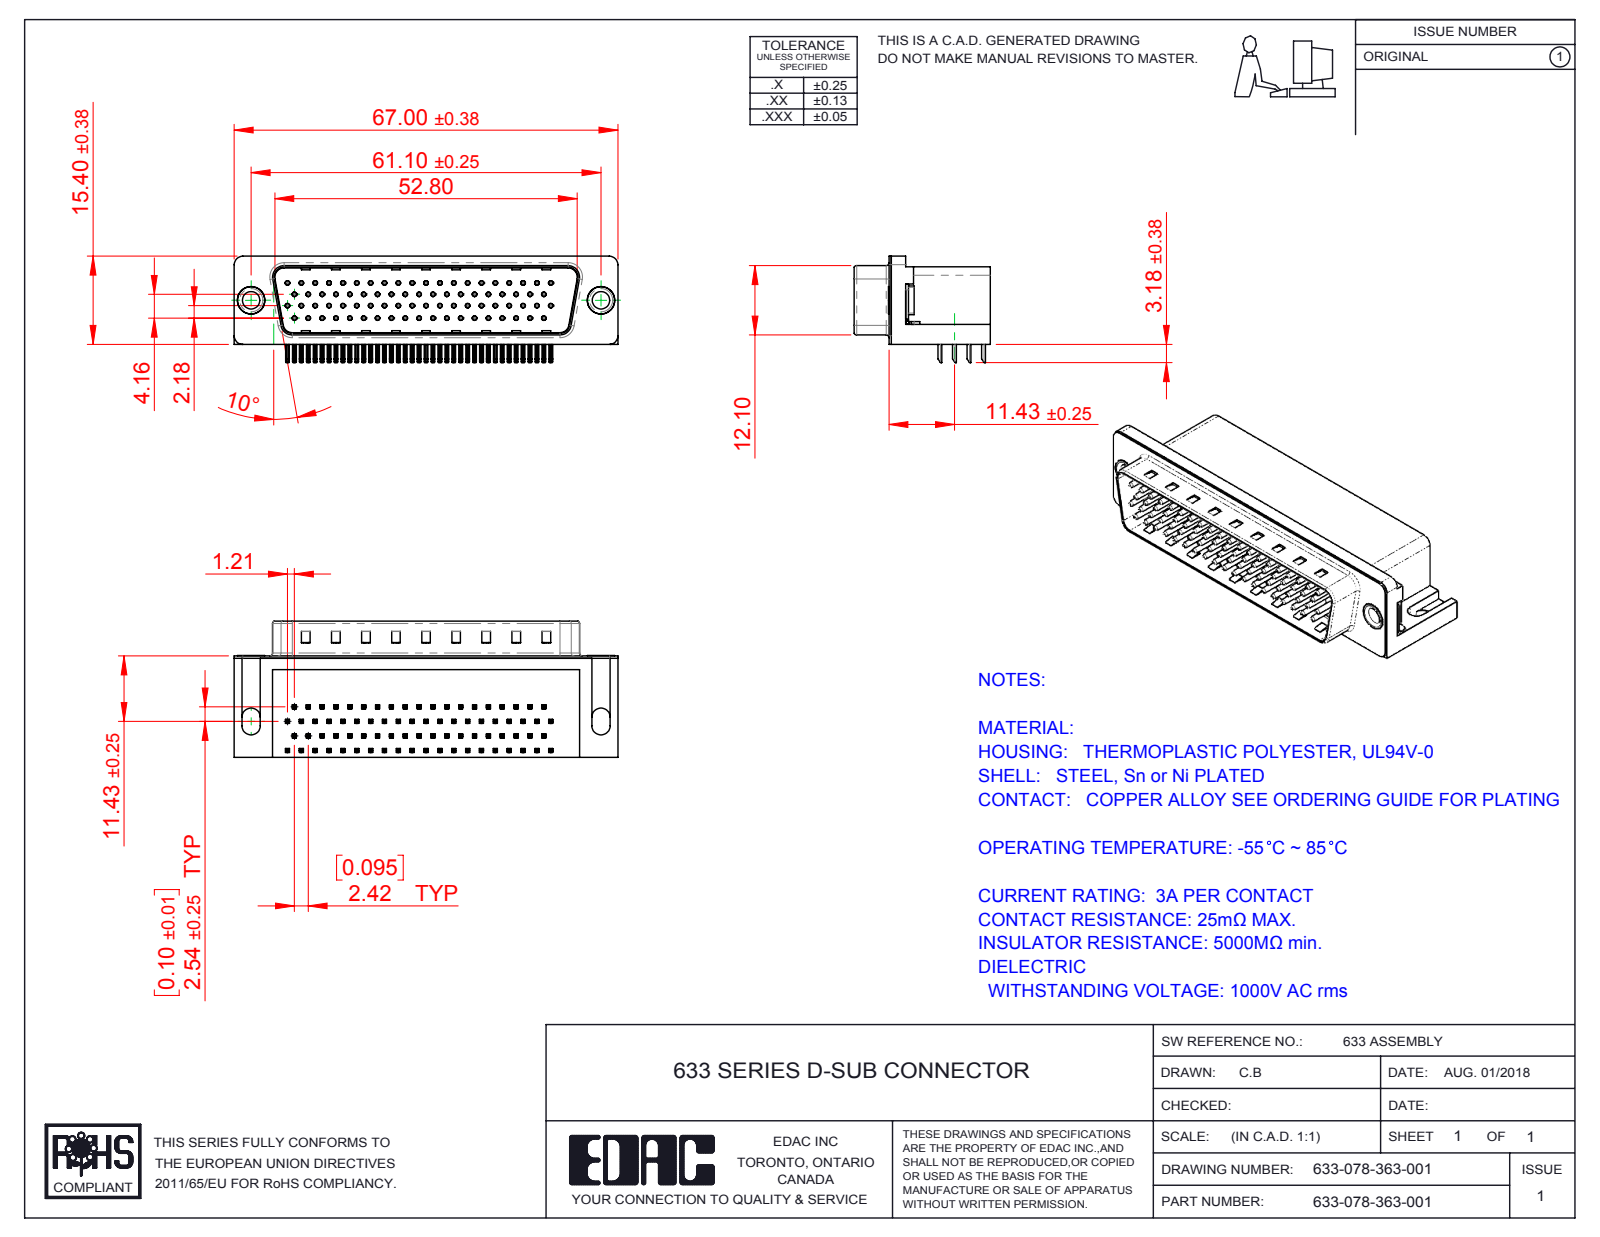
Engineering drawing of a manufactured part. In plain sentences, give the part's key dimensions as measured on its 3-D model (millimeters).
The part is named "633 Contact Middle_78 Contact; 633 Contact Top_78 Contact; 633 Shell_78 Contact; 633 Contact Top 78 (+5 more)". Its 3-D file was written by "SolidWorks 2016 (CONFIG_CONTROL_DESIGN)". It is 84 solids with 6230 faces: 3979 planar, 1756 cylindrical and 495 other. Overall it measures 67 by 23.8 by 18.58 millimeters. Its volume is 14 553 cubic millimeters and its surface area 16 106 square millimeters. Round holes: 78 of diameter 0.35, 78 of diameter 0.8, 2 of diameter 3.05, 2 of diameter 4, 2 of diameter 4.8, 2 of diameter 5. Round bosses or shafts: 78 of diameter 0.75, 2 of diameter 4.9, 2 of diameter 4.75, 2 of diameter 3.85. Partial cylindrical surfaces (rounded edges, fillets, slot ends): 320 of radius 0.25, 156 of radius 0.12, 16 of radius 1, 9 of radius 0.5, 8 of radius 1.6, 6 of radius 1.5, 4 of radius 0.45, 4 of radius 0.9. The main face-to-face distances are 0.4, 13.2, 17.3, 11.7, 13.35, 2.05, 13.75, 1.65, 11.9, 1.85. The hole center spacings are 2.42, 4.84, 7.26, 9.68, 6.26, 7.13, 12.1, 8.62.
